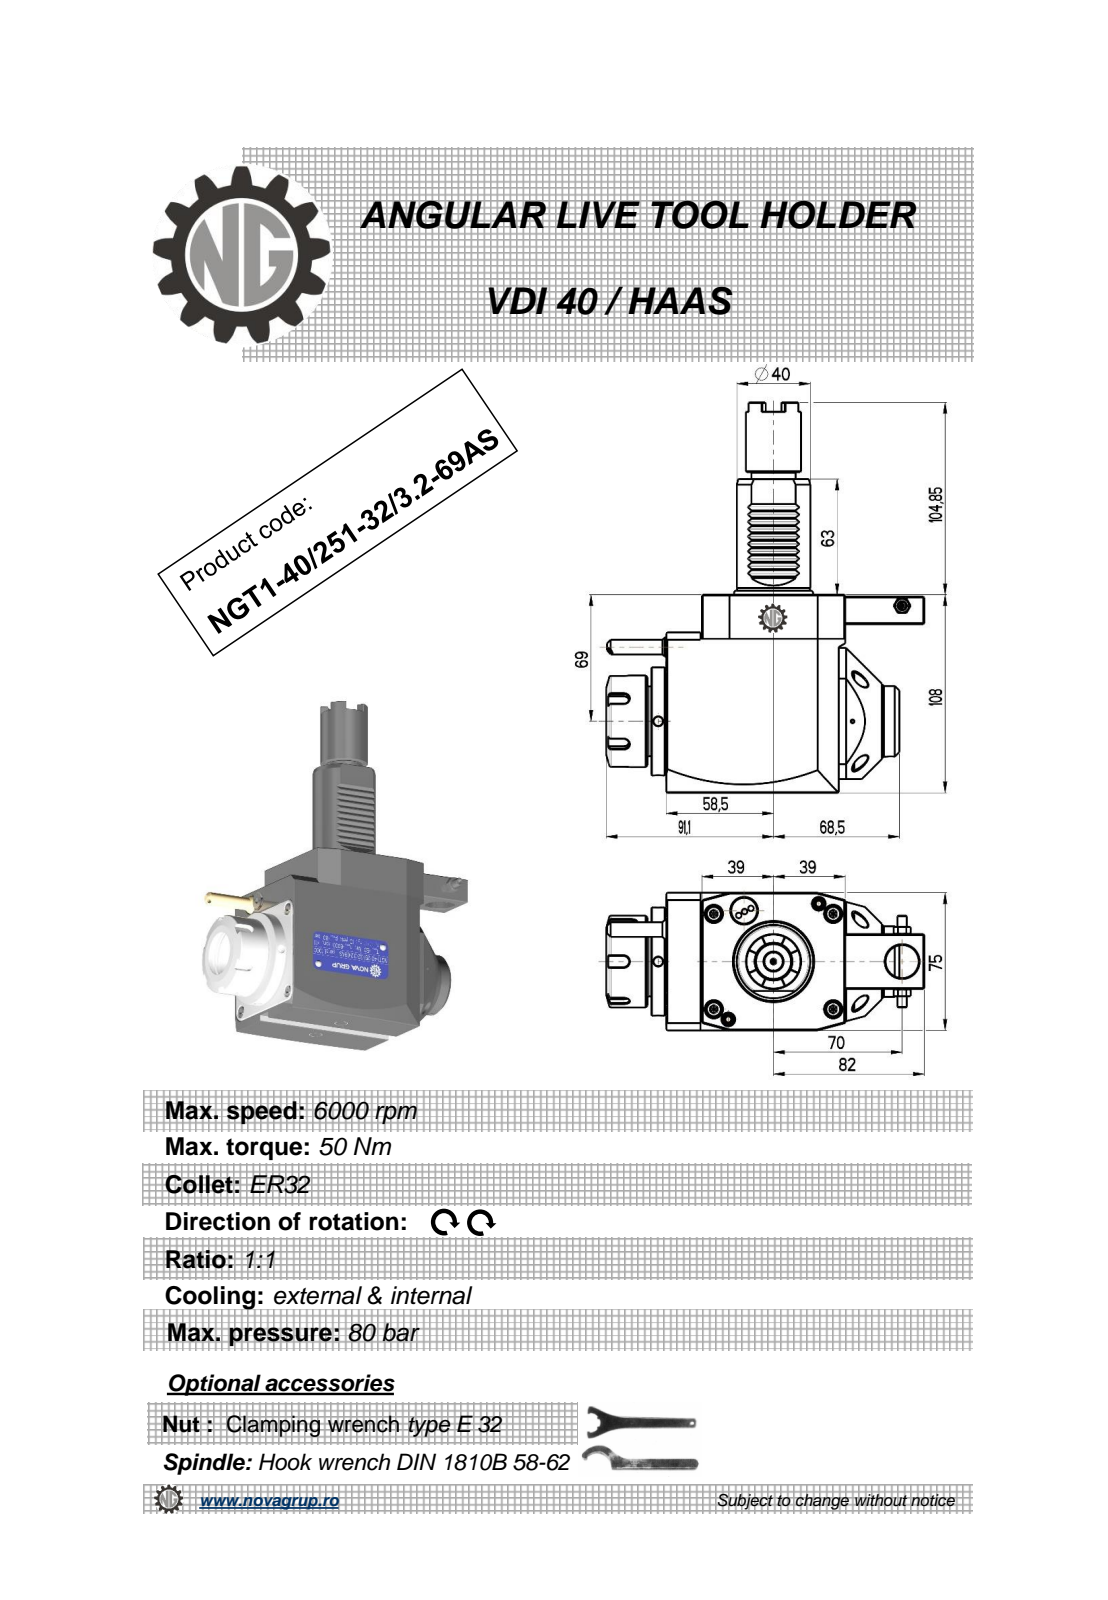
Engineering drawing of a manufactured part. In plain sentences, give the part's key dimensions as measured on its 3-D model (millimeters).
The part is named "NGT1_40_251_32_3_2_69AS". Its 3-D file was written by "PRO/ENGINEER BY PARAMETRIC TECHNOLOGY CORPORATION, 2010280 (CONFIG_CONTROL_DESIGN)". It is 1 solid with 484 faces: 239 planar, 99 cylindrical and 146 other. Overall it measures 212.85 by 173.1 by 75 millimeters. Its volume is 989 494 cubic millimeters and its surface area 82 756 square millimeters. Round holes: 3 of diameter 5, 1 of diameter 3, 1 of diameter 4.2, 1 of diameter 9.5, 1 of diameter 18, 1 of diameter 27, 1 of diameter 46. Round bosses or shafts: 1 of diameter 59, 1 of diameter 50, 1 of diameter 46, 1 of diameter 41, 1 of diameter 40, 1 of diameter 38.5, 1 of diameter 30, 1 of diameter 24. Partial cylindrical surfaces (rounded edges, fillets, slot ends): 12 of radius 0.26, 10 of radius 0.3, 6 of radius 0.2, 5 of radius 3, 2 of radius 5.8, 2 of radius 6, 2 of radius 600, 1 of radius 0.5. The main face-to-face distances are 75, 108, 19.5, 27.5, 1, 3.5, 20, 83.5, 8, 22.5. The hole center spacings are 27.34, 44.12, 61.5, 132.75, 146.94.
